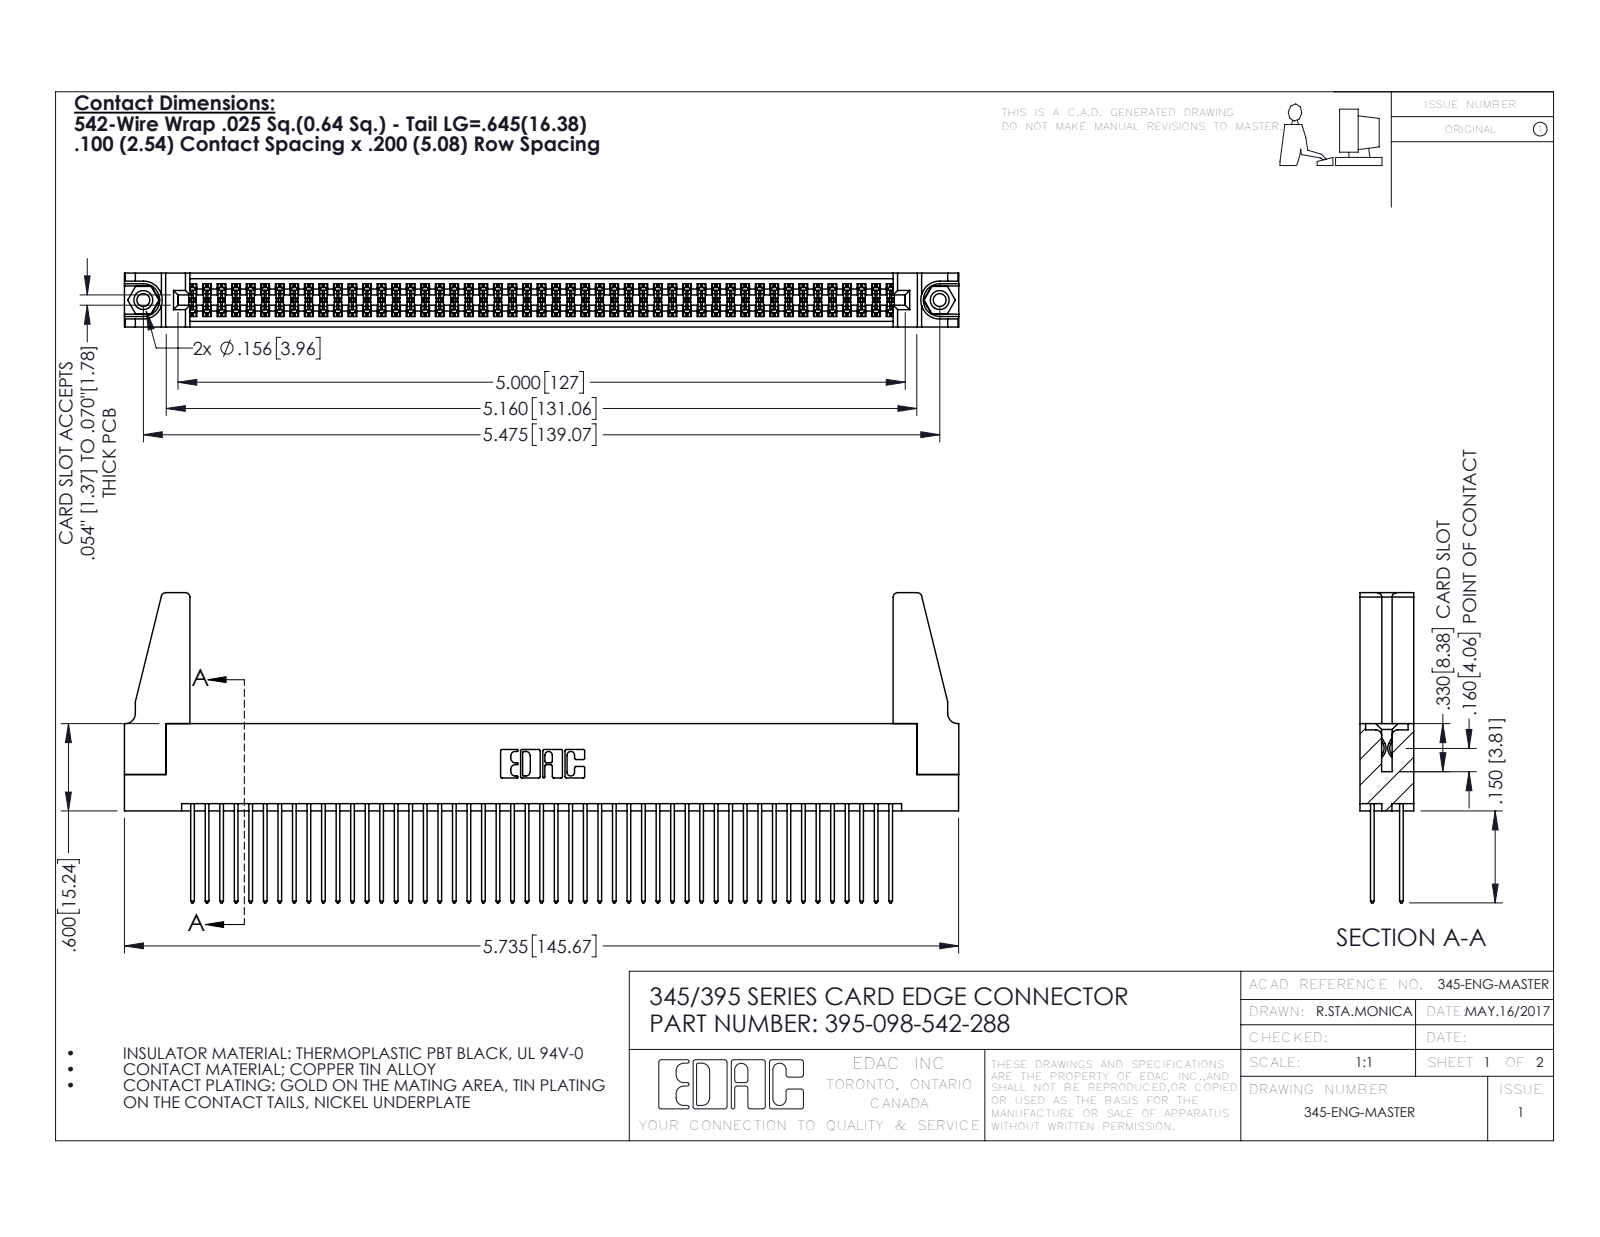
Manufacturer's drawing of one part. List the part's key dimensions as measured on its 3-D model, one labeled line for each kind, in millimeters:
Part name (STEP PRODUCT): 345-292-001_345-293-142; 395-098-542-288; 345-220-078_345-220-088; 345 Part_Flush Mounting Lugs - 0.156 Dia-TH (+1 more)
STEP written by: SolidWorks 2016 (CONFIG_CONTROL_DESIGN)
Units: millimetres
Bodies: 103 solids, 5150 faces (3386 planar, 1748 cylindrical, 16 other)
Overall size (bounding box): 145.7 × 54.2 × 9.4
Volume: 17 930 mm³ · Surface area: 27 080 mm²
Round holes (diameter × count): ⌀2.3 ×2, ⌀3.2 ×2, ⌀4 ×2, ⌀1.6 ×1
Round bosses / shafts (diameter × count): ⌀3.9 ×2
Partial cylindrical surfaces — rounded edges, fillets, slot ends (radius × count): R0.2 ×147, R0.3 ×98, R0.3 ×22, R0.8 ×8, R0.2 ×6, R0.8 ×6, R0.7 ×3, R0.4 ×2
Main face-to-face distances: 1.8, 7.6, 5.1, 2.5, 6.9, 0.6, 9.4, 5.7, 4.4, 3.8
Hole centre spacings: 6.9, 133.1, 139.1
